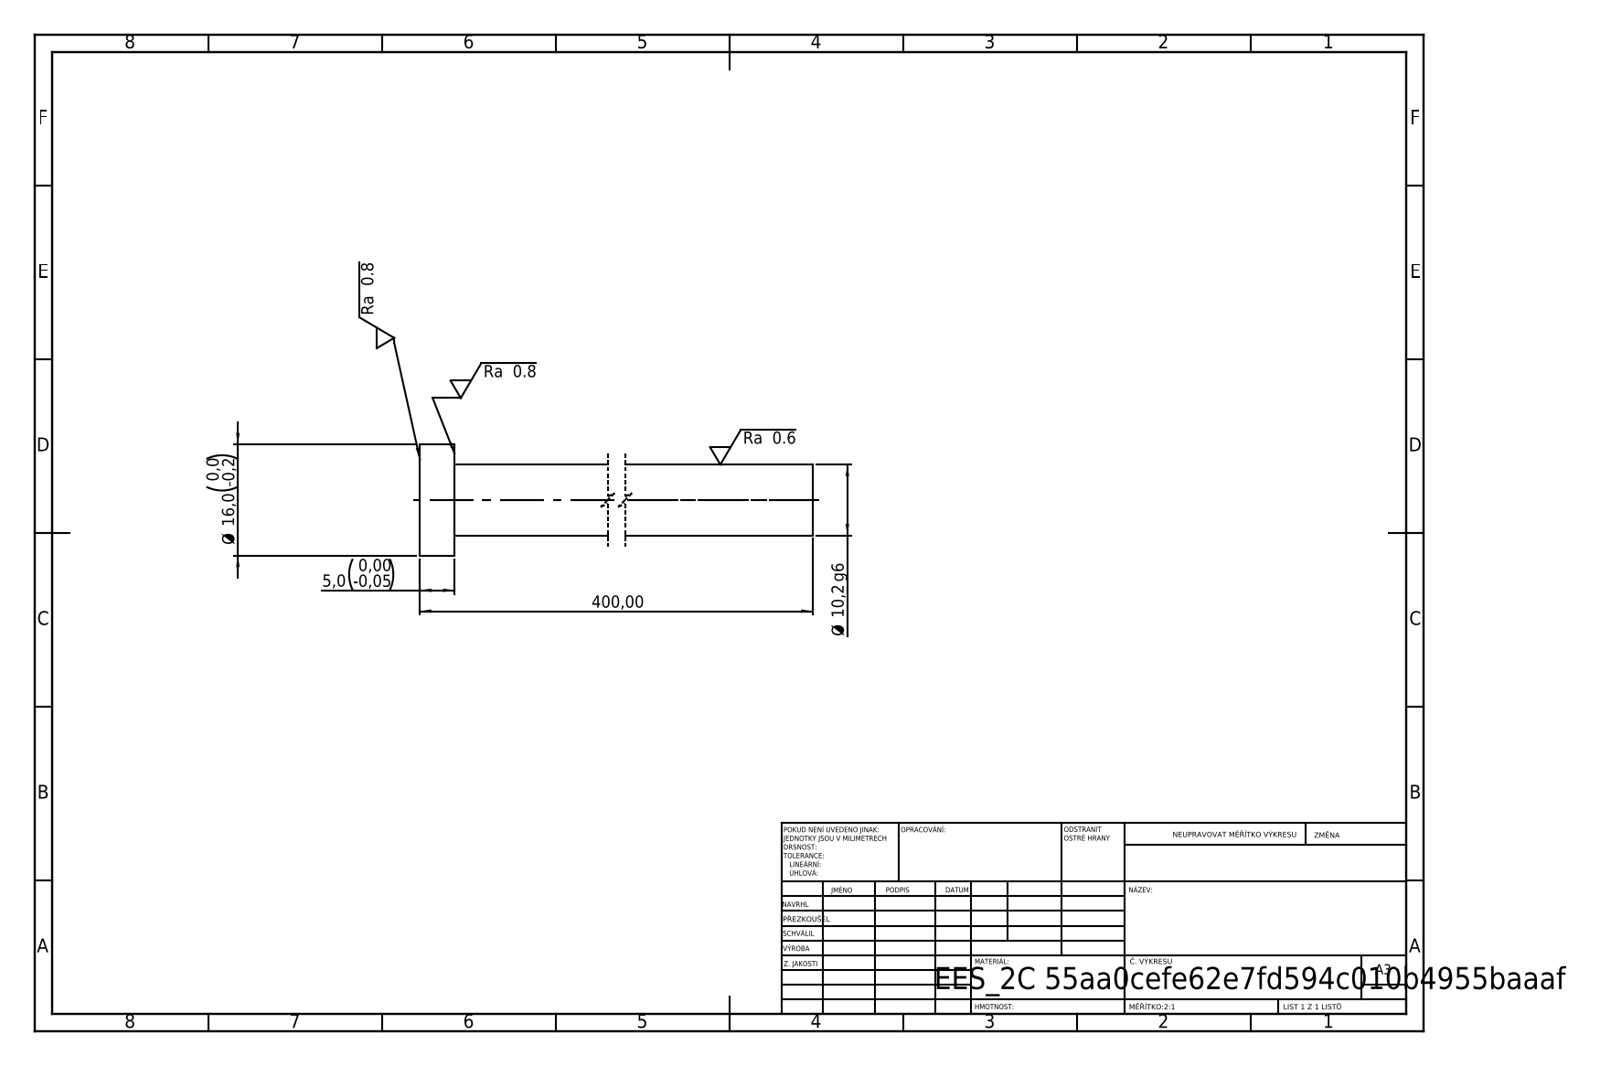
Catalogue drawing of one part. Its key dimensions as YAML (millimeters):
step_written_by: "SolidWorks 2019 (CONFIG_CONTROL_DESIGN)"
units: millimeters
bodies: {solids: 1, faces: 7, planar: 3, cylindrical: 4, other: 0}
overall_size: [400, 16, 16]
volume: 33282
surface_area: 13311
round_bosses_or_shafts:
  - {diameter: 16, count: 1}
  - {diameter: 10.2, count: 1}
face_to_face_distances: [5, 400, 395]
